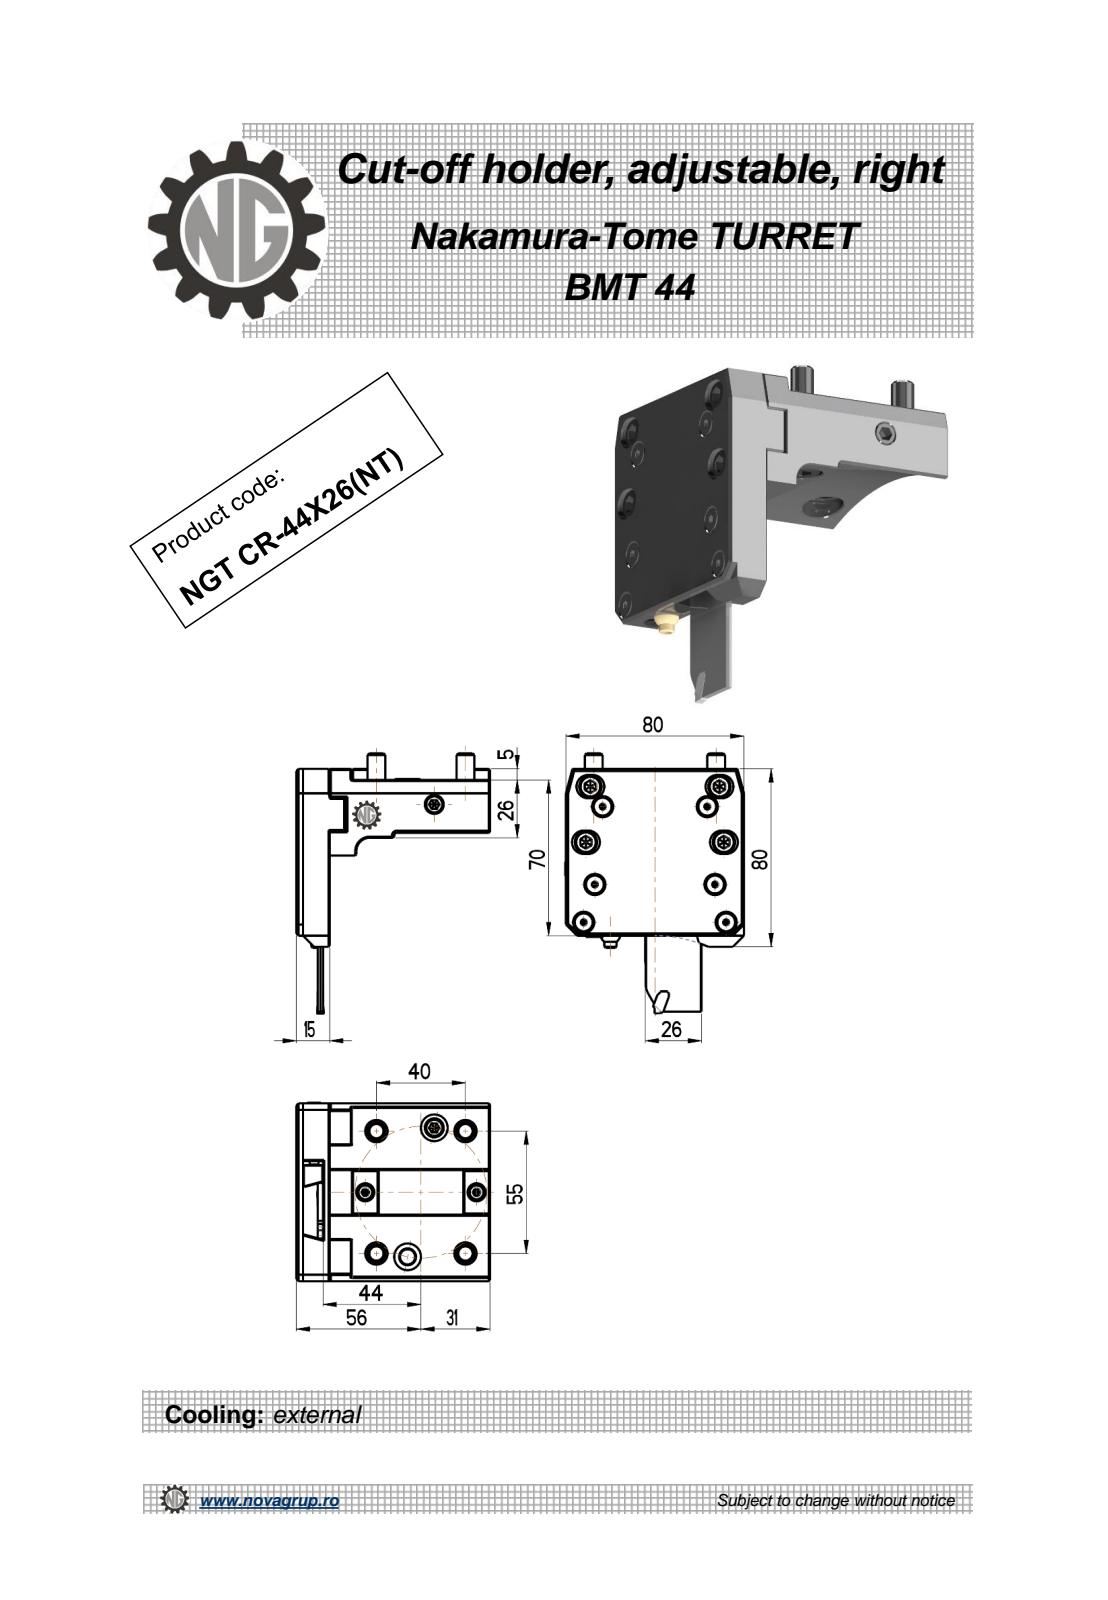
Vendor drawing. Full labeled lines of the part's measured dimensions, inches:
Part name (STEP PRODUCT): NGT_CR_44_26_NT
STEP written by: PRO/ENGINEER BY PARAMETRIC TECHNOLOGY CORPORATION, 2010280 (CONFIG_CONTROL_DESIGN)
Units: inches
Bodies: 1 solid, 487 faces (295 planar, 110 cylindrical, 82 other)
Overall size (bounding box): 3.443 × 3.425 × 3.16
Volume: 12.18 in³ · Surface area: 74.26 in²
Round holes (diameter × count): ⌀0.197 ×2, ⌀0.315 ×2, ⌀0.472 ×2, ⌀0.138 ×1, ⌀0.268 ×1
Round bosses / shafts (diameter × count): ⌀0.315 ×5, ⌀0.394 ×4, ⌀0.157 ×3, ⌀0.217 ×1
Partial cylindrical surfaces — rounded edges, fillets, slot ends (radius × count): R0.008 ×24, R0.012 ×12, R0.207 ×8, R0.006 ×6, R0.006 ×6, R0.016 ×6, R0.039 ×1, R0.236 ×1
Main face-to-face distances: 0.118, 0.472, 0.591, 0.197, 0.394, 3.15, 0.354, 2.953, 0.866, 1.024
Hole centre spacings: 1.535, 2.097, 2.332, 2.503
